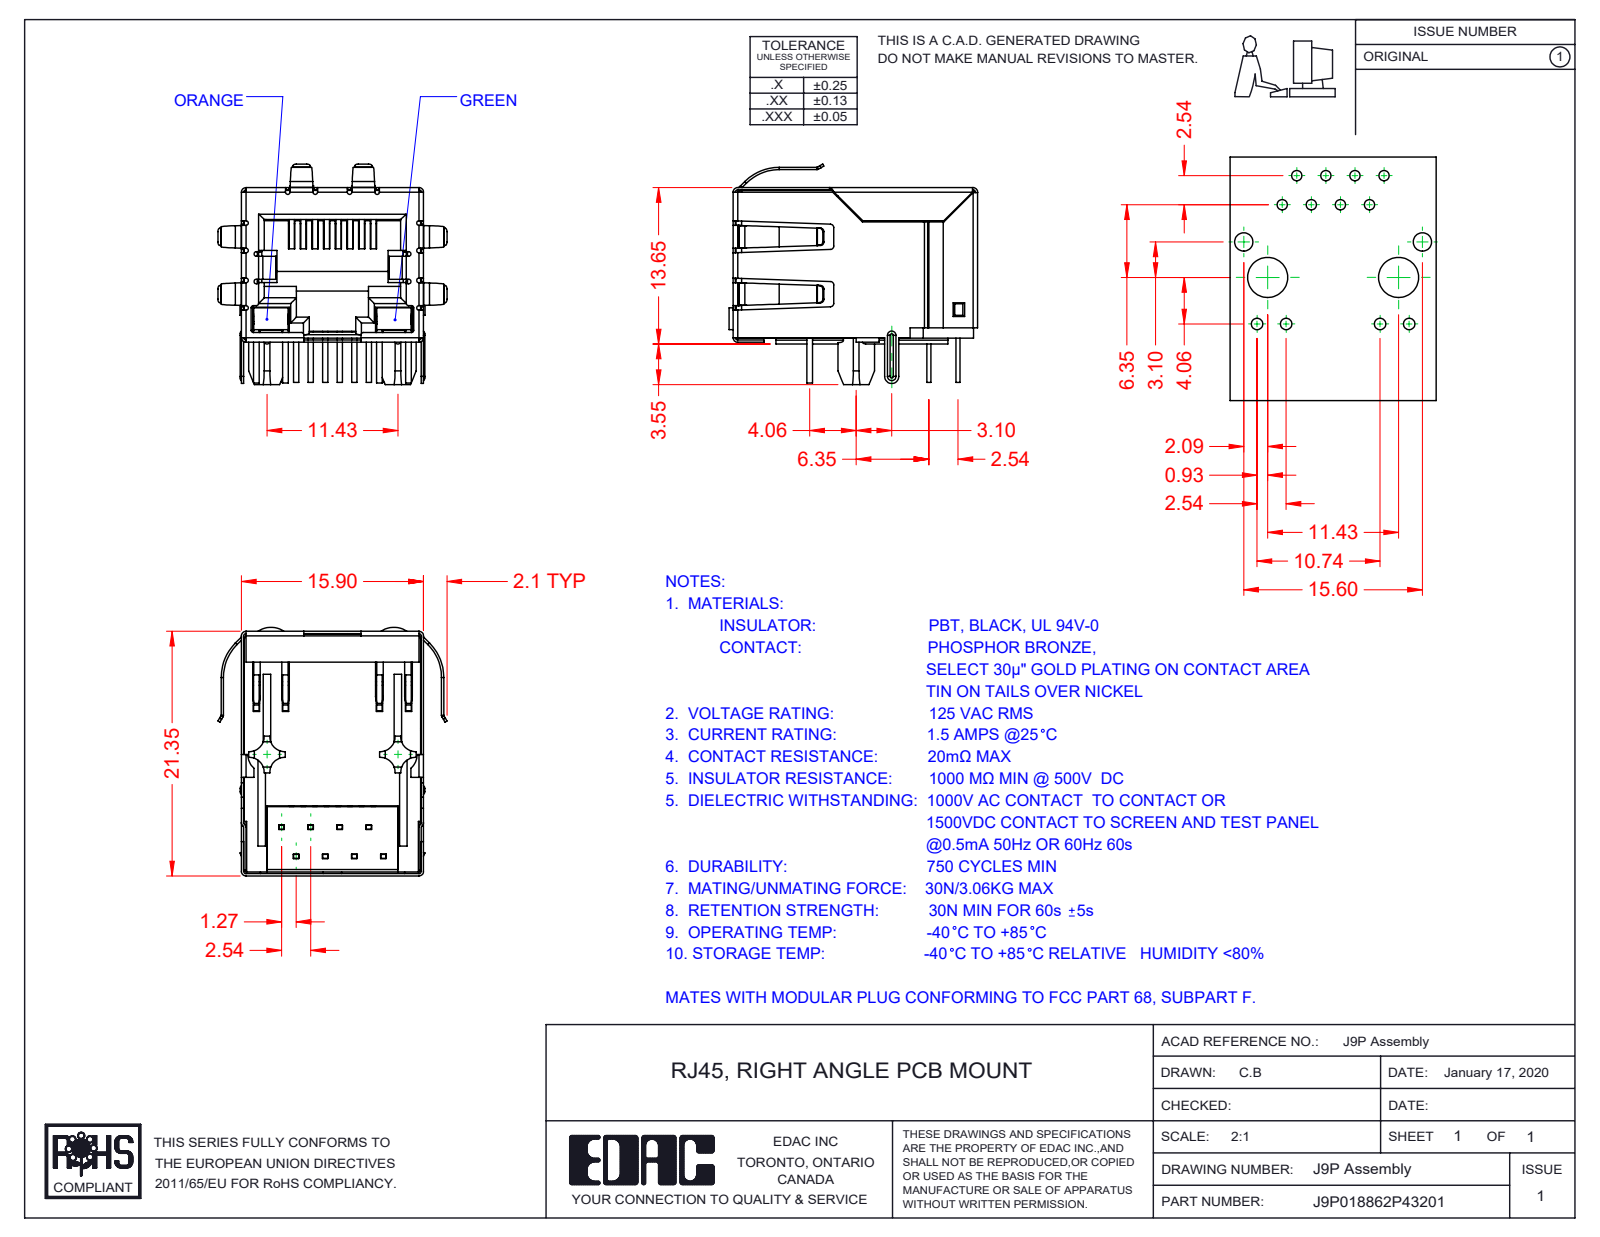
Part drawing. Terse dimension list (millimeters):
name: 9P-LED LED LH_4-Orange; 9P-LED Assembly; 9P-LED Contacts; 9P-LED LED RH_3-Green (+4 more)
written by: SolidWorks 2016 (CONFIG_CONTROL_DESIGN)
unit: mm
bodies: 13 solids, 1472 faces (1042 planar, 336 cylindrical, 94 other)
size: 21.7 × 20 × 19.25
volume: 2 687 mm³; area: 7 515 mm²
rounds: 39× R0.2, 22× R0.5, 20× R0.3, 16× R0.4, 8× R1.3, 5× R0.23, 4× R0.11, 4× R0.31
face distances: 15.45, 15.7, 15.65, 0.35, 0.54, 15.5, 12.36, 0.6, 1.4, 0.59
